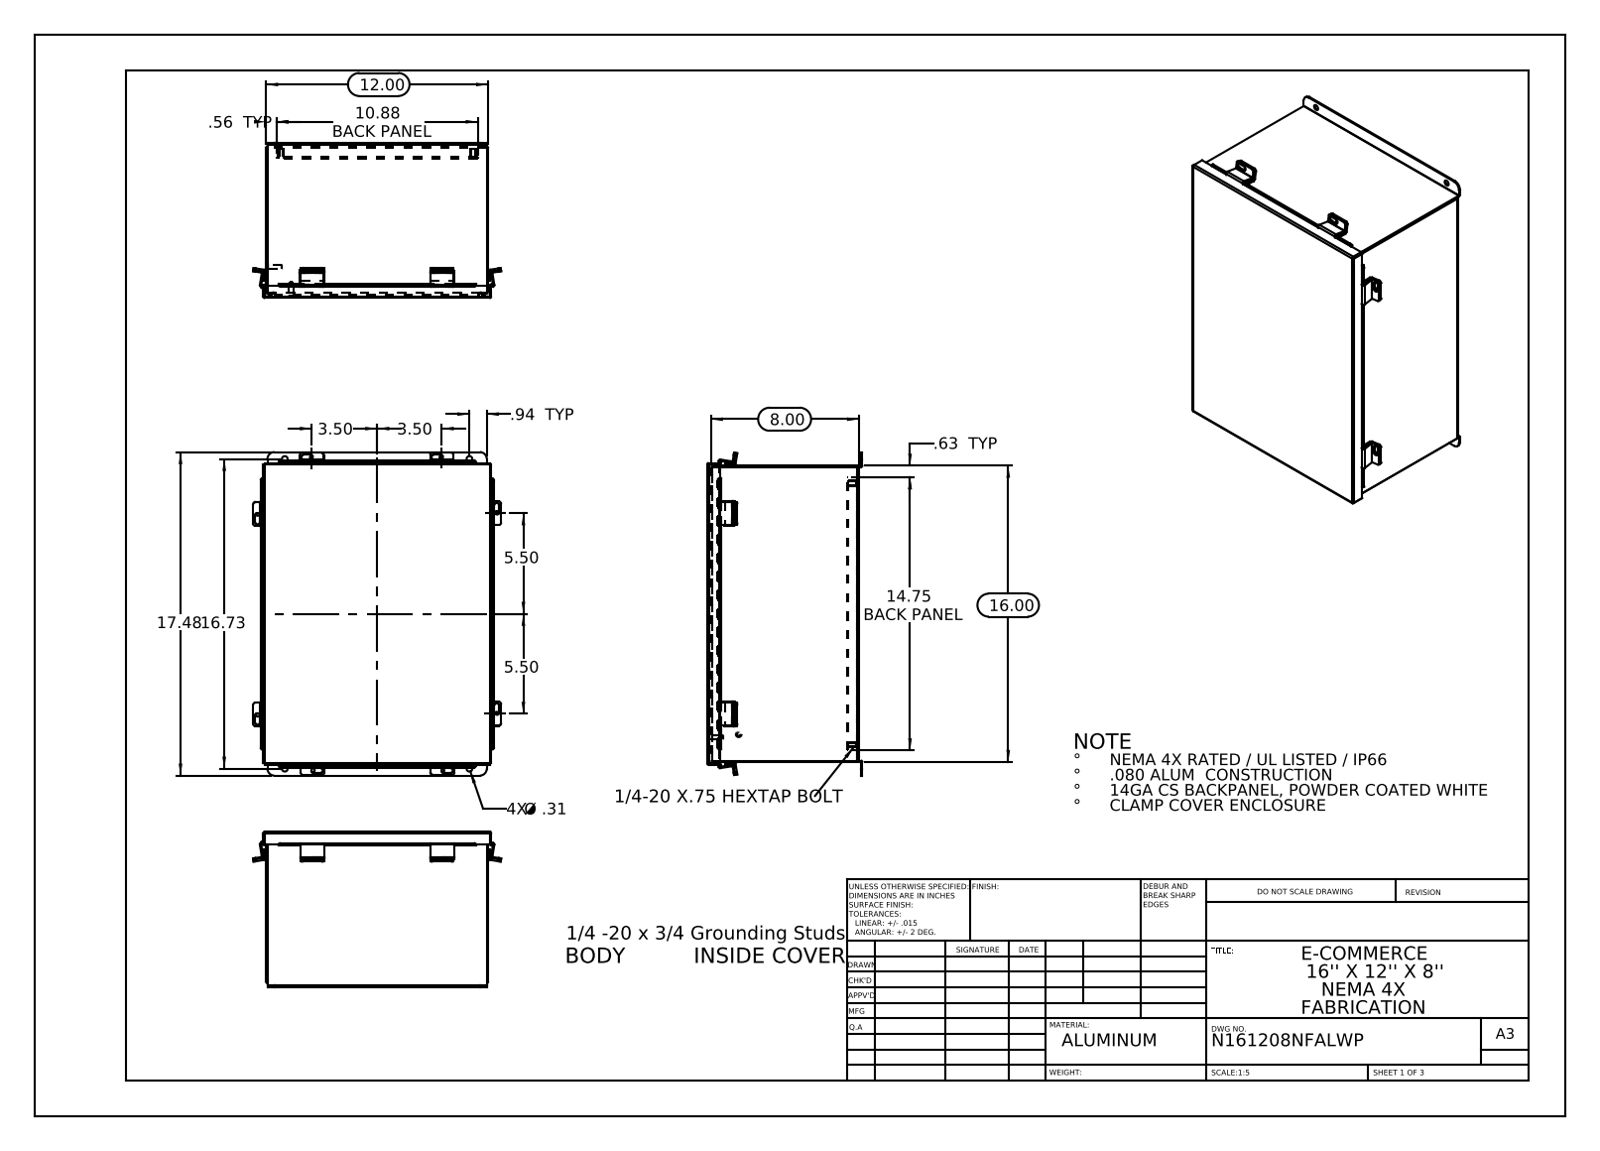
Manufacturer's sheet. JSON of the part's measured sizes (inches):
{"part_name": "N161208NFSSWP JIC Backpanel; N161208NFSSWP JIC Cover Clamp; N161208NFSSWP JIC Clamp Bracket; N161208NFSSWP JIC_Standoff (+6 more)", "step_written_by": "SolidWorks 2013 (CONFIG_CONTROL_DESIGN)", "units": "inches", "bodies": {"solids": 27, "faces": 640, "planar": 420, "cylindrical": 200, "other": 20}, "overall_size": [17.476, 13.407, 8.39], "volume_in3": 82.16, "surface_area_in2": 2222, "round_holes": [[0.25, 12], [0.187, 4], [0.312, 4]], "round_bosses_or_shafts": [[0.313, 4], [0.315, 2], [0.236, 2]], "partial_cylinders_radius": [[0.125, 32], [0.009, 16], [0.133, 16], [0.013, 12], [0.088, 12], [0.083, 8], [0.1, 8], [0.084, 4]], "face_to_face_distances": [0.075, 8.128, 11.925, 15.925, 8.053, 8.203, 7.628, 0.575, 0.5, 7.553], "hole_center_spacings": [1.315, 10.258, 15.427, 18.48, 7, 9.976, 10.375, 10.85]}
